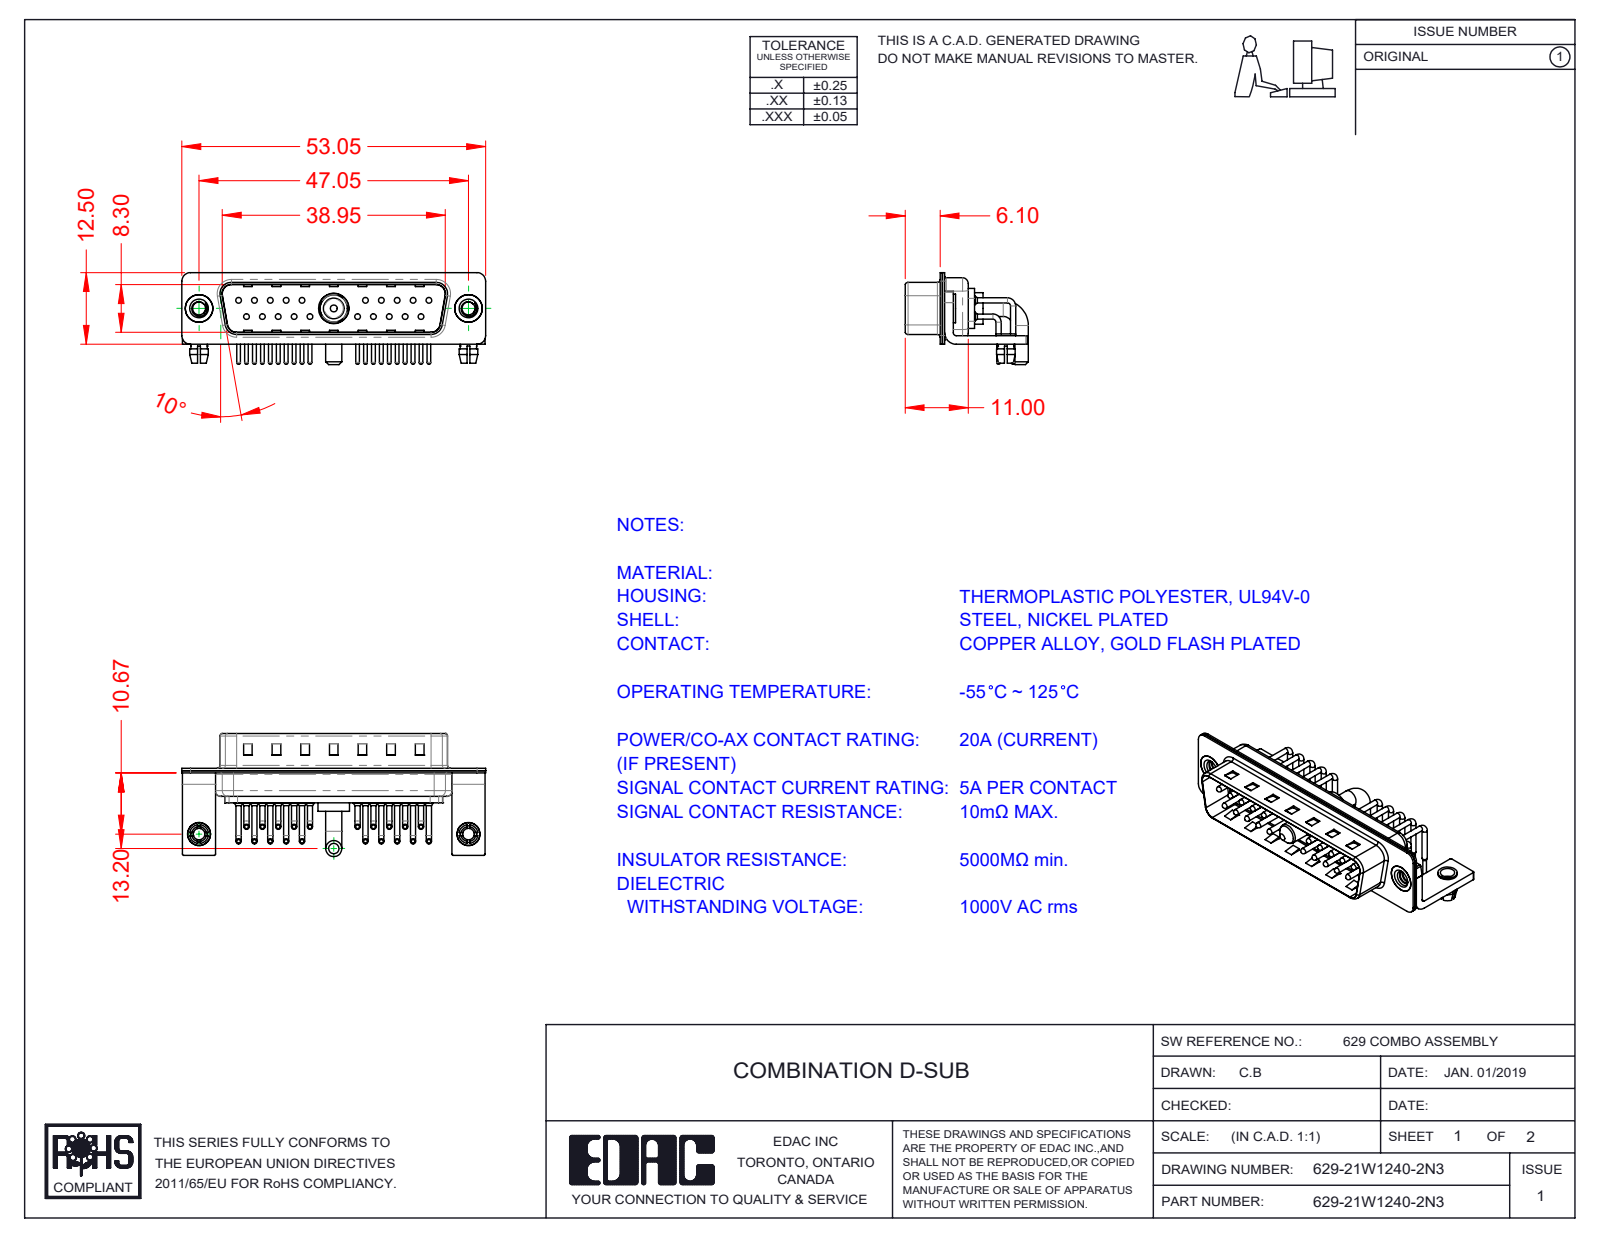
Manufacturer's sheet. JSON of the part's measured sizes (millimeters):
{"part_name": "629Combo Board Lock; 629Combo Housing_21W1; 629Combo Stabilizer Bracket; 629Combo Threaded Rivet_3 (+6 more)", "step_written_by": "SolidWorks 2020 (CONFIG_CONTROL_DESIGN)", "units": "millimeters", "bodies": {"solids": 31, "faces": 2751, "planar": 1529, "cylindrical": 928, "other": 294}, "overall_size": [53.05, 21.5, 16.05], "volume_mm3": 3322, "surface_area_mm2": 8392, "round_holes": [[2, 22], [0.75, 20], [1.6, 20], [2.26, 2], [2.5, 2], [3.2, 2], [4, 2], [4.8, 2], [4.85, 1], [5.3, 1]], "round_bosses_or_shafts": [[0.9, 40], [1.5, 20], [1, 20], [0.65, 20], [5, 2], [4.9, 2], [4, 2], [3.4, 2]], "partial_cylinders_radius": [[1.01, 20], [0.25, 16], [1.5, 16], [2, 13], [0.5, 9], [1.6, 8], [0.6, 4], [0.65, 4]], "face_to_face_distances": [0.4, 0.8, 9.5, 1.5, 9.1, 8.7, 9.9, 0.6, 2.1, 0.75], "hole_center_spacings": [3.16, 2.77, 5.54, 8.31, 5.04, 19.39, 20.97, 22.16]}
